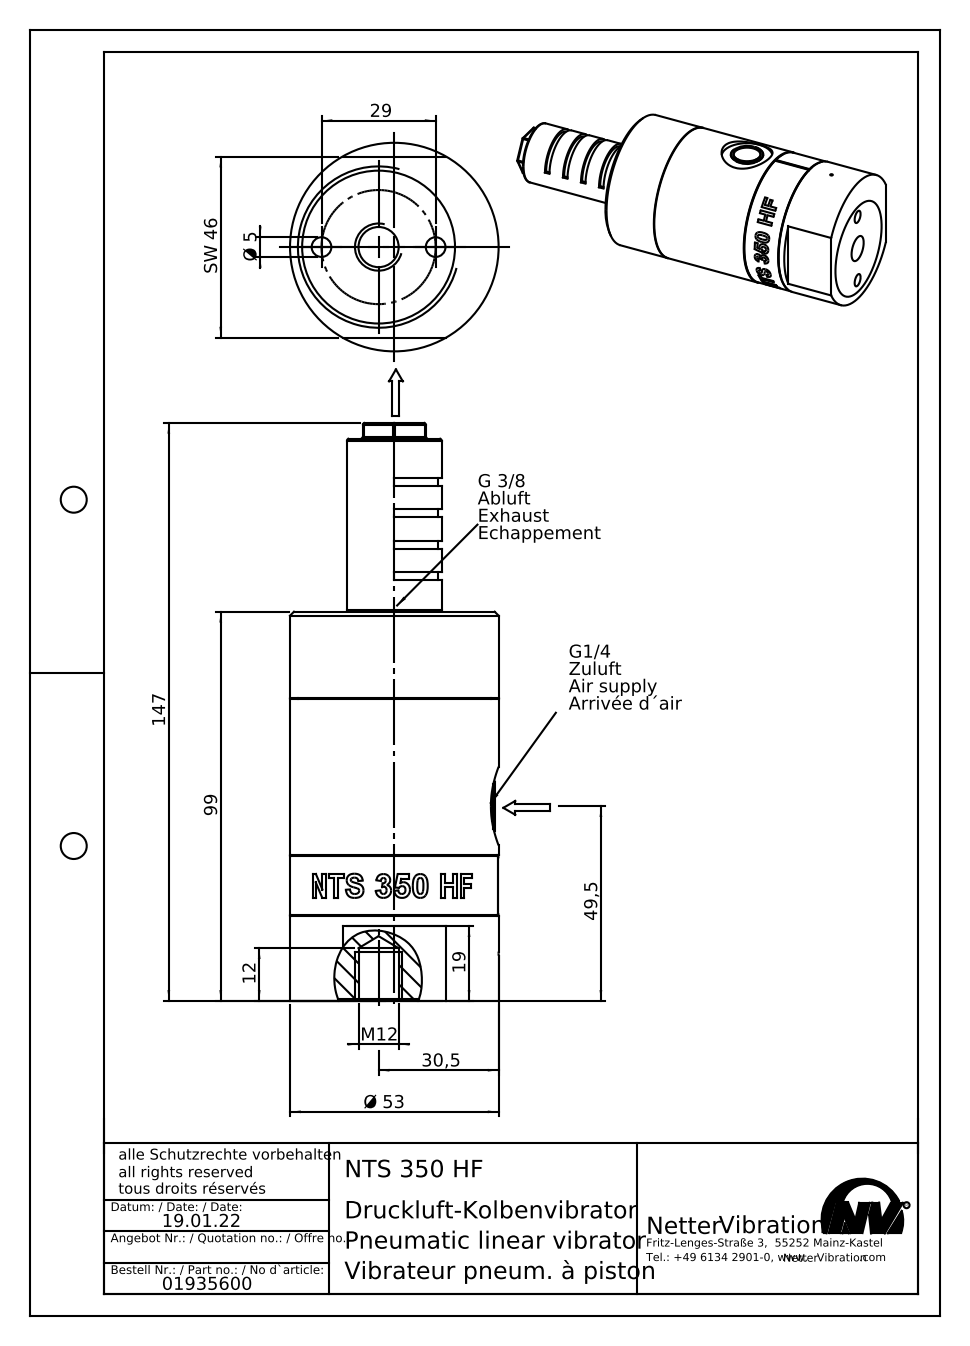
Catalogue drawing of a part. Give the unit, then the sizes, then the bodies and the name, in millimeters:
Units: millimetres
Overall size (bounding box): 146.9 × 53 × 53
Round holes (diameter × count): ⌀3 ×5, ⌀1 ×2, ⌀5 ×2, ⌀10.2 ×1, ⌀11.5 ×1, ⌀15.25 ×1, ⌀15.4 ×1, ⌀20 ×1, ⌀38.84 ×1, ⌀41.5 ×1, ⌀47.5 ×1, ⌀52.4 ×1
Round bosses / shafts (diameter × count): ⌀53 ×1, ⌀52.8 ×1, ⌀48.9 ×1, ⌀48.5 ×1, ⌀47 ×1, ⌀41 ×1, ⌀24 ×1, ⌀21.5 ×1
Partial cylindrical surfaces — rounded edges, fillets, slot ends (radius × count): R0.5 ×22, R11 ×1
Main face-to-face distances: 56.9, 22, 78.9, 66, 9.3, 12.9, 9.1, 66.2, 12.7, 17
Hole centre spacings: 14.38, 14.5, 16.36, 18.7, 20, 21.5, 33.73, 35.1
Volume: 239 464 mm³ · Surface area: 52 549 mm²
Bodies: 5 solids, 313 faces (92 planar, 162 cylindrical, 59 other)
Part name (STEP PRODUCT): NTS 350 HF Kolbenvibrator #01935600
STEP written by: SolidWorks 2015 (AUTOMOTIVE_DESIGN)
